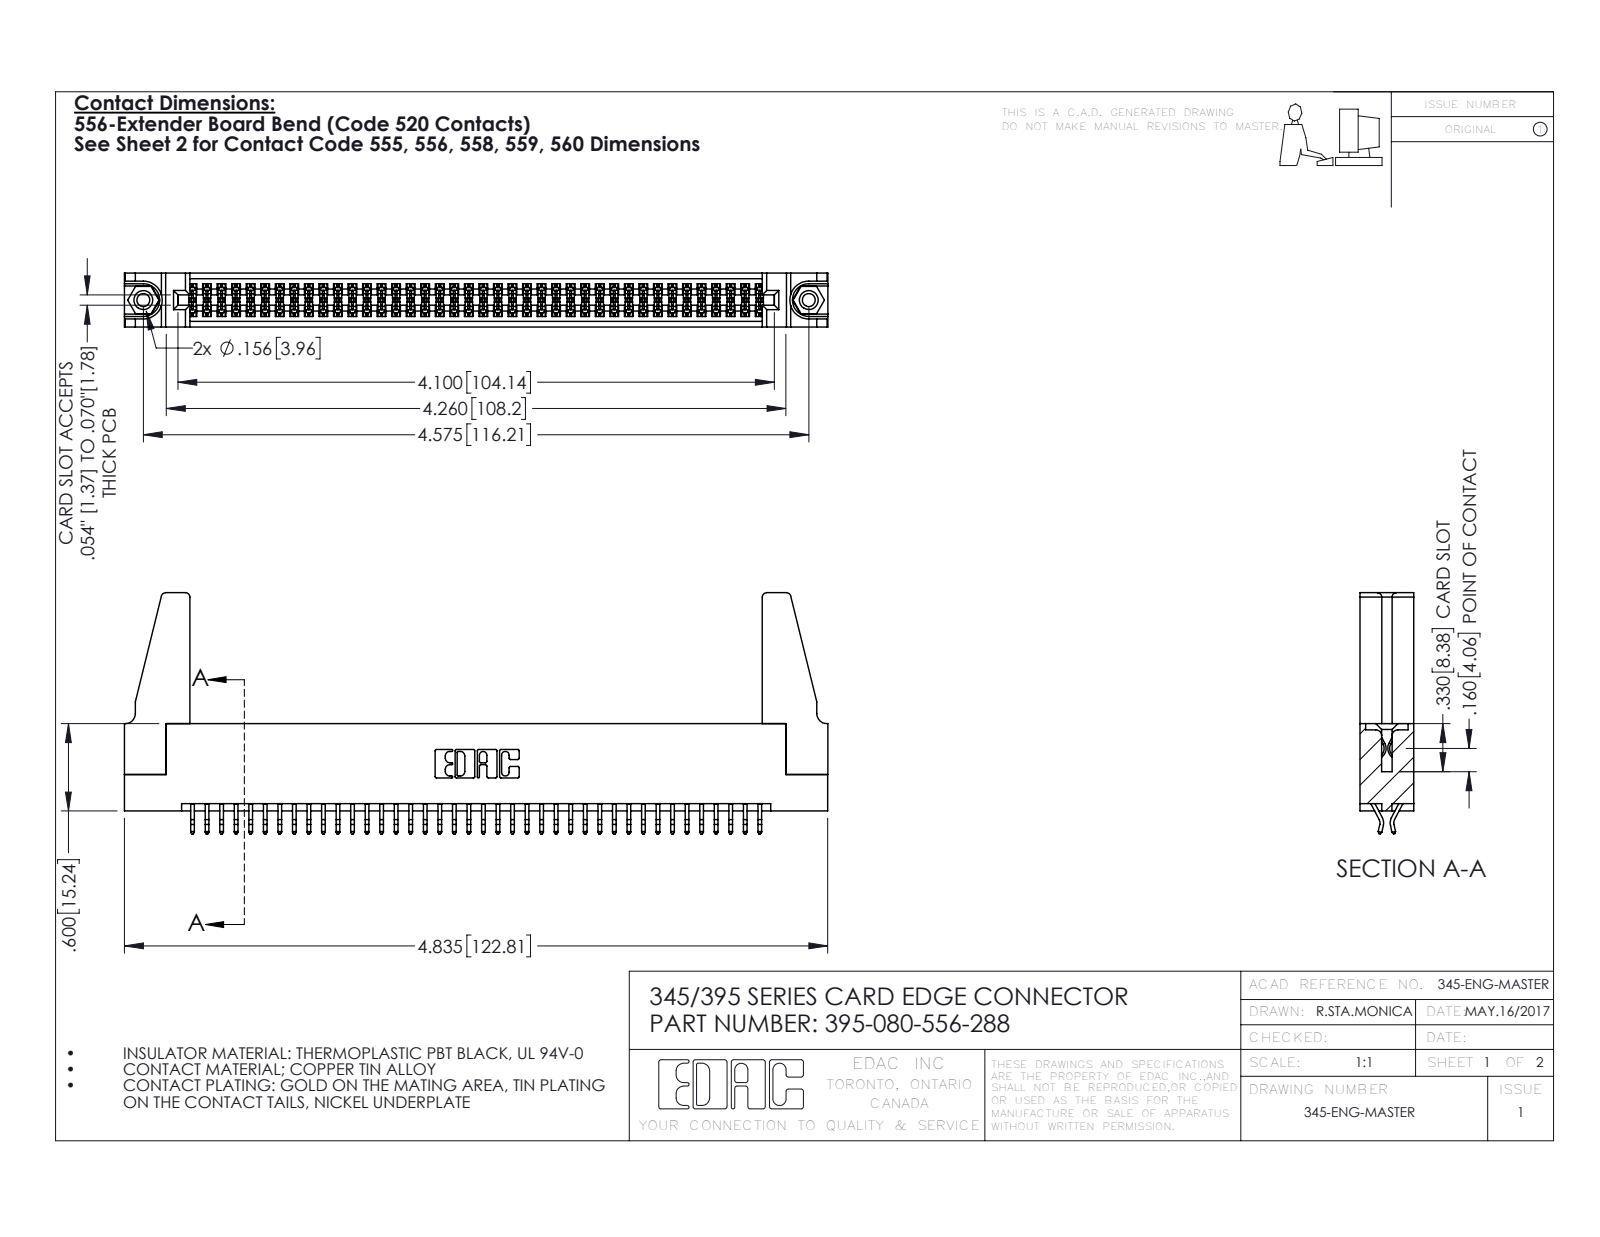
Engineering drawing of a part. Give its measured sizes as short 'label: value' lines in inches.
name: 395-080-556-288; 345 Part_Flush Mounting Lugs - 0.156 Dia-TH; 345-220-078_345-220-088; 345-292-001_556 Tail (+1 more)
written by: SolidWorks 2016 (CONFIG_CONTROL_DESIGN)
unit: in
bodies: 85 solids, 4730 faces (3112 planar, 1602 cylindrical, 16 other)
size: 4.836 × 1.657 × 0.37
volume: 0.925 in³; area: 31.96 in²
holes: 2× ⌀0.089, 2× ⌀0.125, 2× ⌀0.156, 1× ⌀0.064
bosses: 2× ⌀0.155
rounds: 120× R0.006, 22× R0.01, 8× R0.03, 6× R0.007, 6× R0.031, 3× R0.026, 2× R0.01, 2× R0.014
face distances: 0.072, 0.298, 0.37, 0.2, 0.025, 0.098, 0.272, 0.225, 0.175, 0.149
hole spacings: 0.27, 4.339, 4.575
